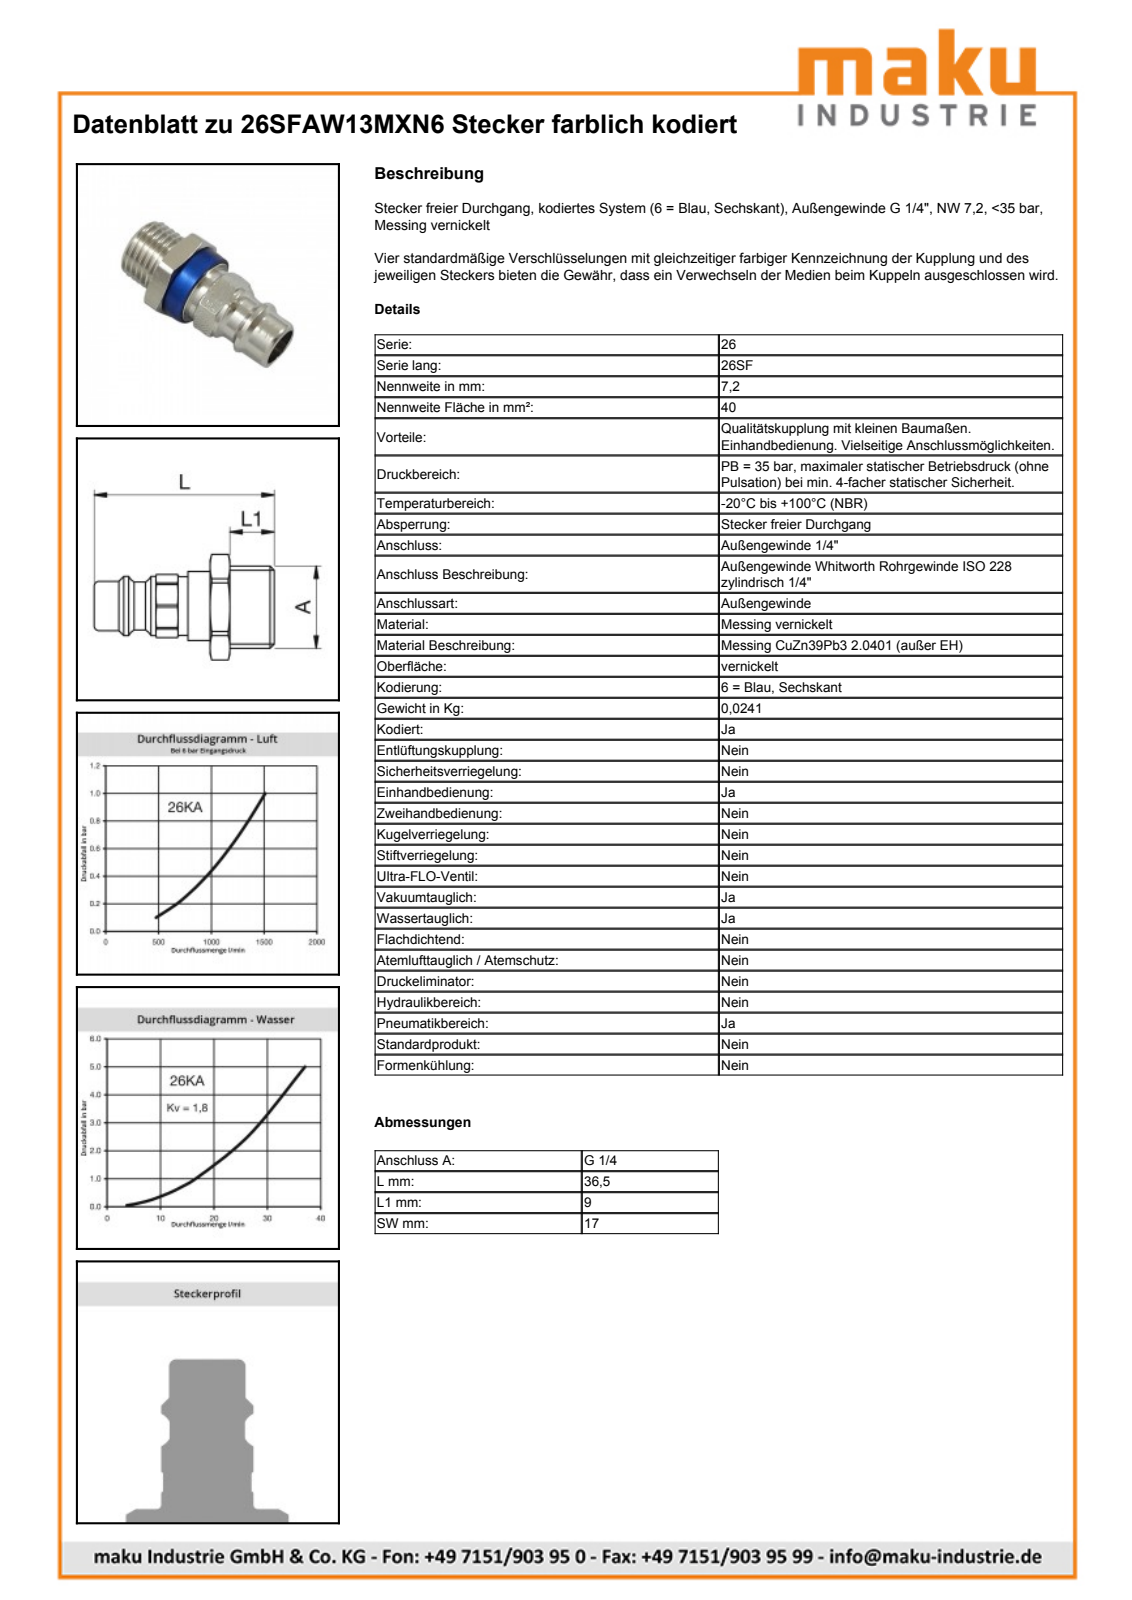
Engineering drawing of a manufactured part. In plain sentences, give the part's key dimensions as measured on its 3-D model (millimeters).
The part is named "D107806; D107805; D103012". Its 3-D file was written by "Autodesk Inventor 2013 (AUTOMOTIVE_DESIGN)". It is 2 solids with 76 faces: 19 planar, 23 cylindrical and 34 other. Overall it measures 36.5 by 19.15 by 17 millimeters. Its volume is 3 115 cubic millimeters and its surface area 3 196 square millimeters. Round holes: 1 of diameter 7.85, 1 of diameter 13.85, 1 of diameter 14.05. Round bosses or shafts: 1 of diameter 15.5, 1 of diameter 14, 1 of diameter 13.16, 1 of diameter 12, 1 of diameter 11.9, 1 of diameter 10, 1 of diameter 9.75. Partial cylindrical surfaces (rounded edges, fillets, slot ends): 1 of radius 6.8, 1 of radius 9.57. The main face-to-face distances are 2.5, 14.5, 17, 4, 12, 4.5, 8.5, 17.5, 13, 9.
